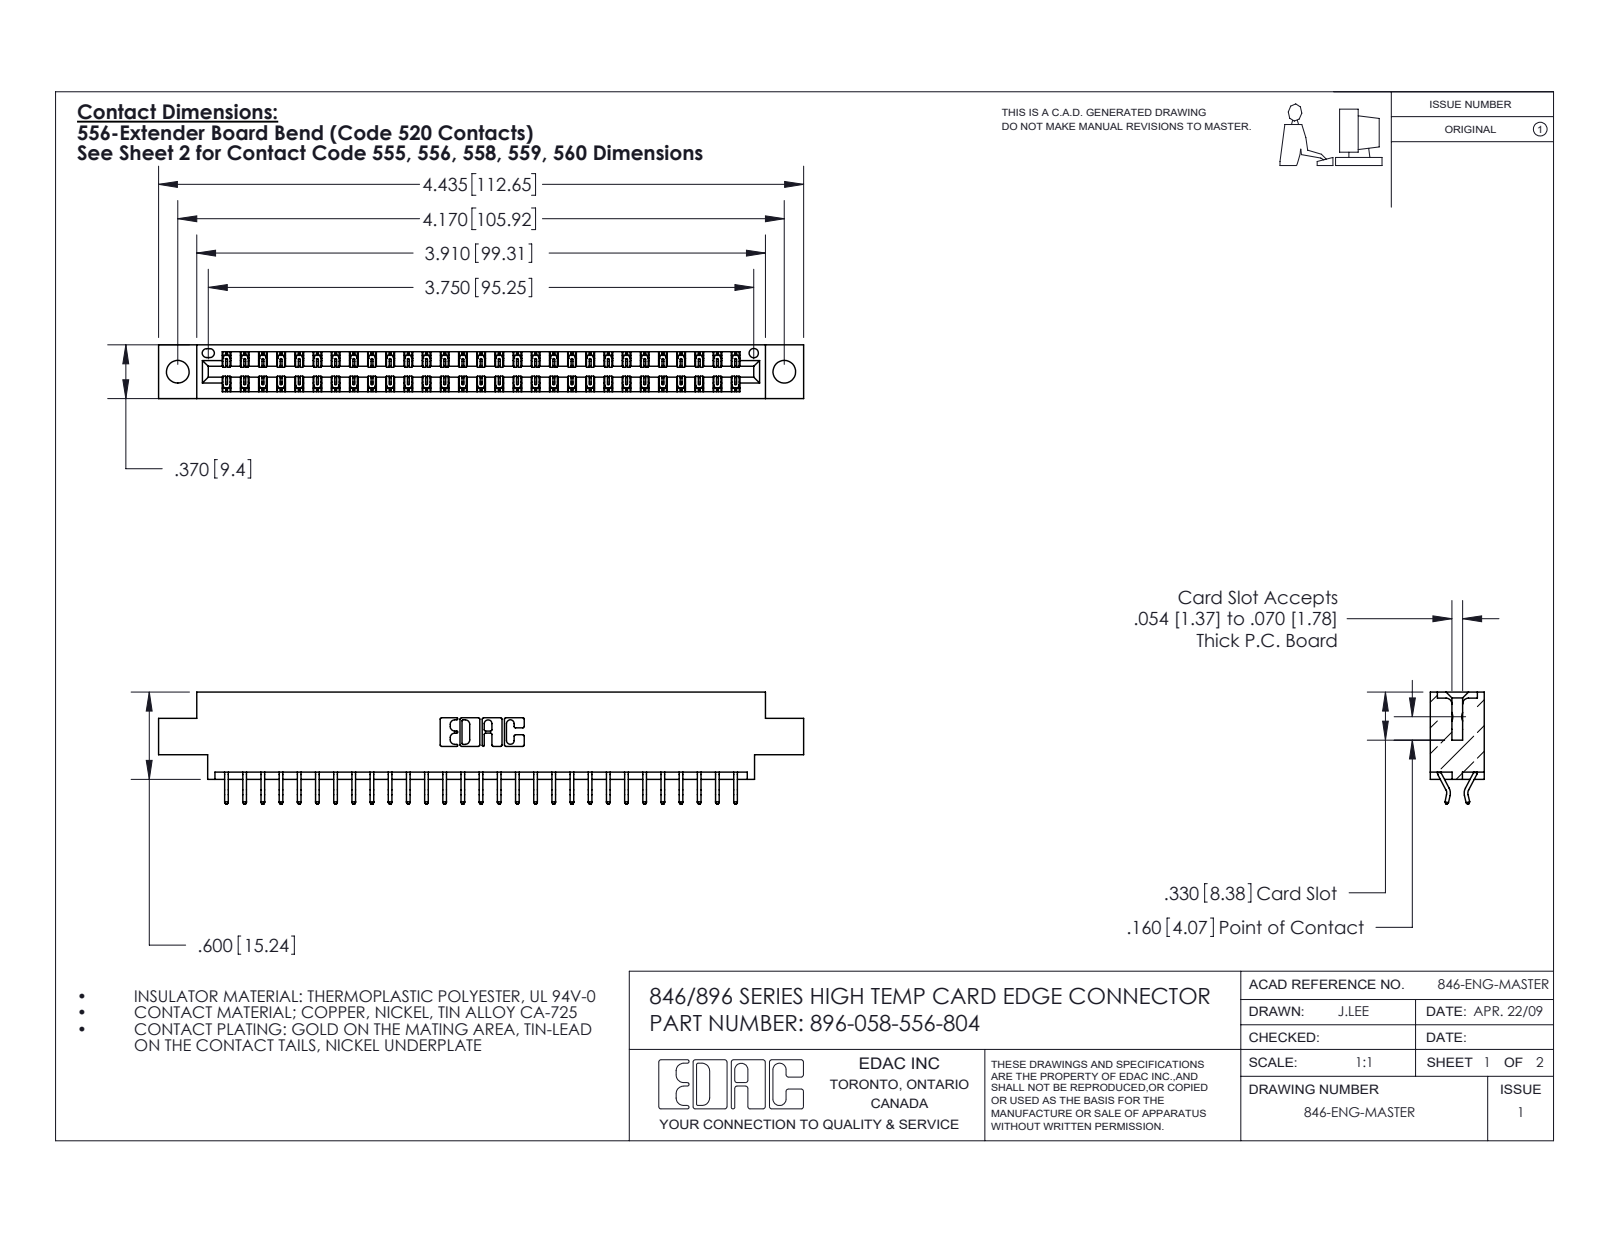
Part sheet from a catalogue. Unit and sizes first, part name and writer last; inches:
Units: inches
Overall size (bounding box): 4.435 × 0.77 × 0.37
Round holes (diameter × count): ⌀0.156 ×2, ⌀0.064 ×1
Partial cylindrical surfaces — rounded edges, fillets, slot ends (radius × count): R0.006 ×87, R0.01 ×22, R0.007 ×6, R0.031 ×6, R0.026 ×3, R0.01 ×2, R0.014 ×2, R0.022 ×2
Main face-to-face distances: 0.048, 0.322, 0.37, 0.25, 0.025, 0.072, 0.298, 0.275, 0.148, 0.222
Hole centre spacings: 0.246, 3.962, 4.17
Volume: 0.649 in³ · Surface area: 22.26 in²
Bodies: 59 solids, 3490 faces (2342 planar, 1148 cylindrical, 0 other)
Part name (STEP PRODUCT): 396-058-556-804; 346 Part_0.170 Offset - 0.156 Dia-TH; 345-292-001_556 Tail
STEP written by: SolidWorks 2016 (CONFIG_CONTROL_DESIGN)
